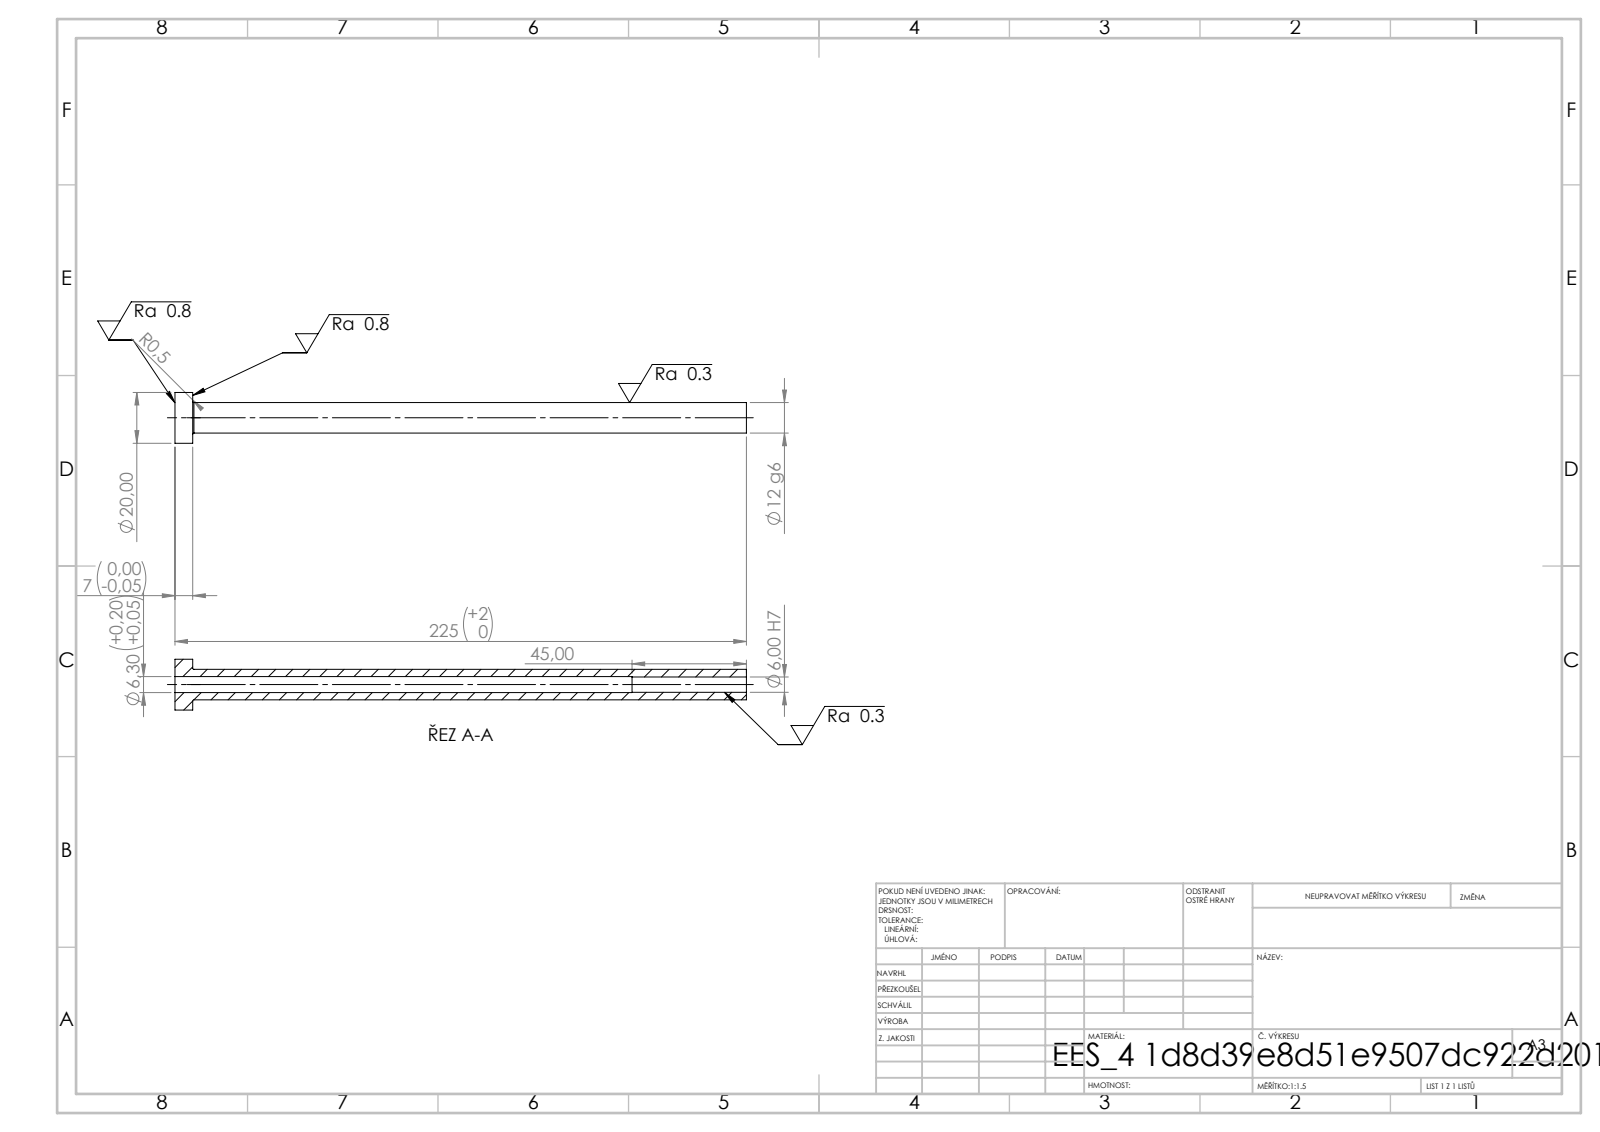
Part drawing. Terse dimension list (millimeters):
written by: SolidWorks 2019 (CONFIG_CONTROL_DESIGN)
unit: mm
bodies: 1 solid, 14 faces (4 planar, 8 cylindrical, 2 other)
size: 225 × 20 × 20
volume: 19 973 mm³; area: 13 633 mm²
holes: 1× ⌀6, 1× ⌀6.3
bosses: 1× ⌀20, 1× ⌀12
face distances: 7, 225, 218, 180, 173, 45
